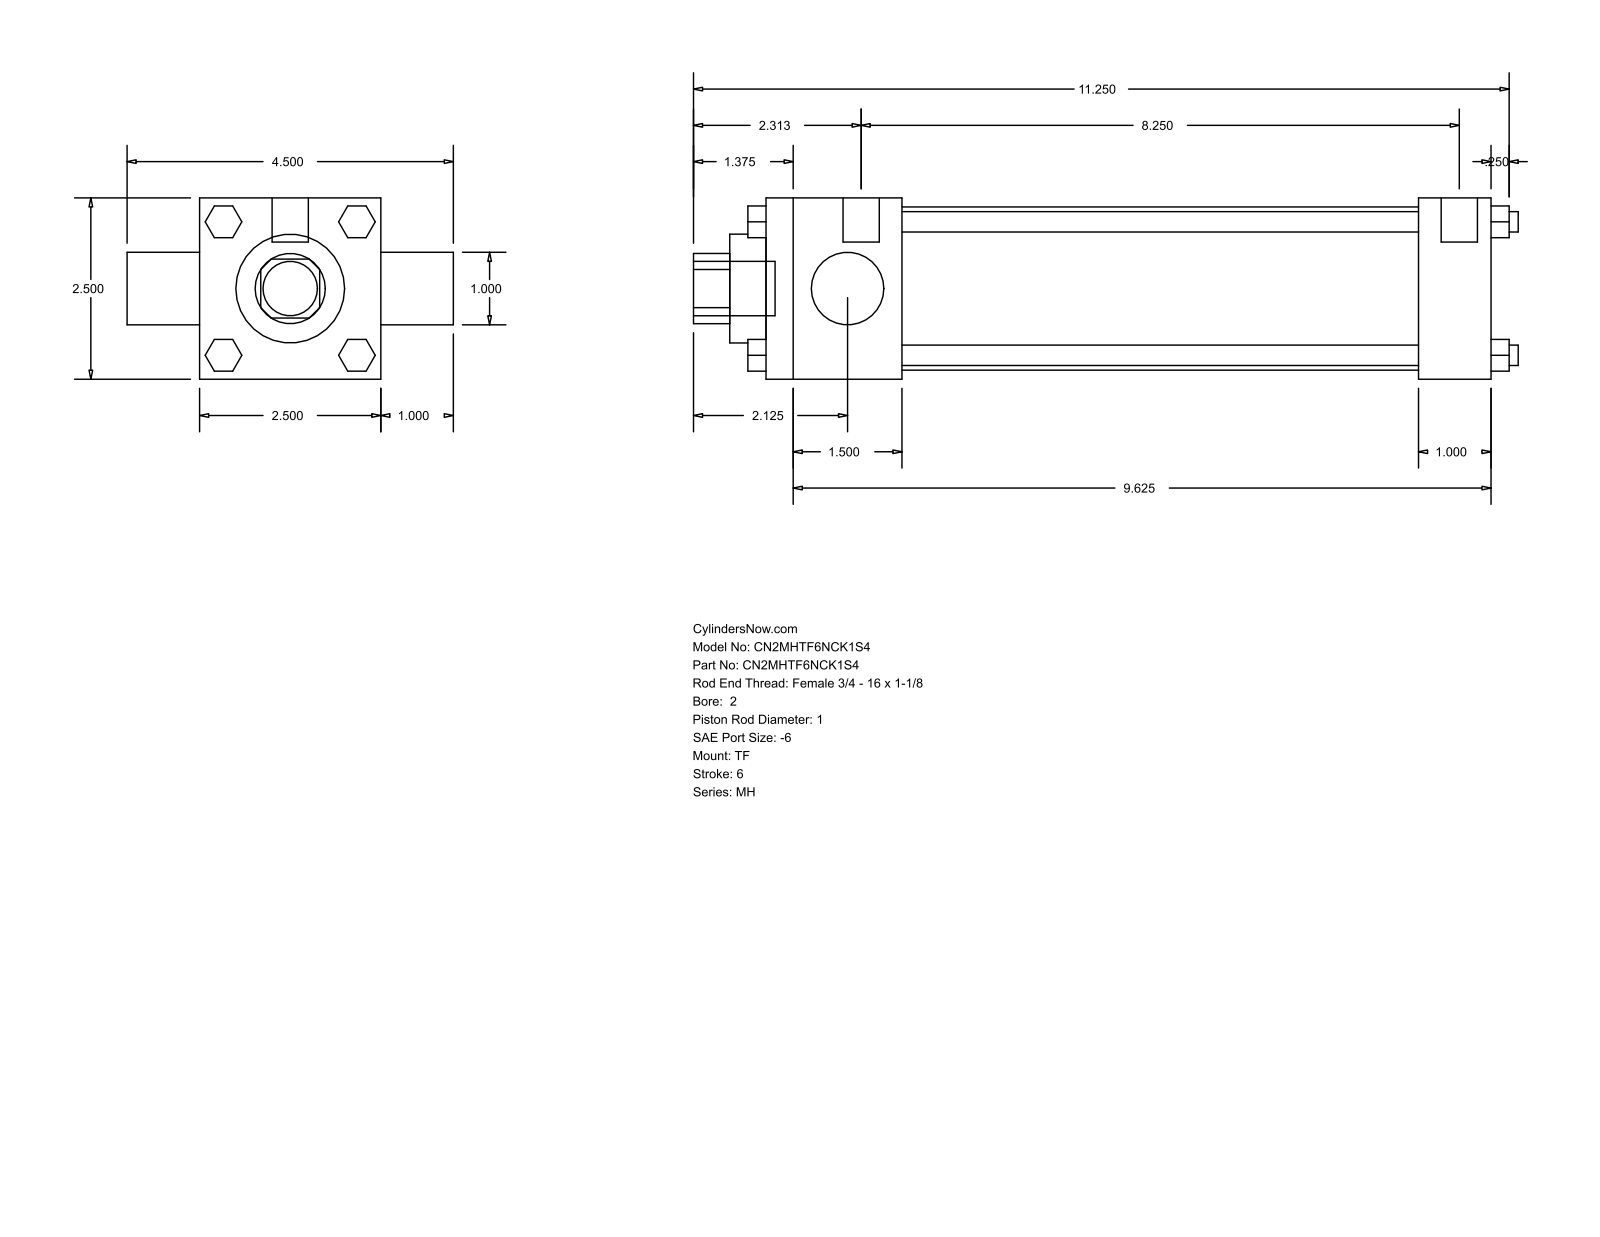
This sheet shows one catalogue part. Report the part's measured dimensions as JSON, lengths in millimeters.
{"part_name": "MH_TF__0200_1", "step_written_by": "GSSL Pune (CONFIG_CONTROL_DESIGN)", "units": "millimeters", "bodies": {"solids": 0, "faces": 120, "planar": 92, "cylindrical": 28, "other": 0}, "overall_size": [288.93, 114.3, 63.5], "round_holes": [[25.4, 2], [38.1, 1], [57.15, 1]], "round_bosses_or_shafts": [[7.14, 4], [5.56, 3], [12.7, 2], [19.05, 1]], "partial_cylinders_radius": [[12.29, 1]], "face_to_face_distances": [63.5, 254, 25.4, 47.63, 228.6, 180.97, 206.37, 88.9, 266.7, 6.35]}
